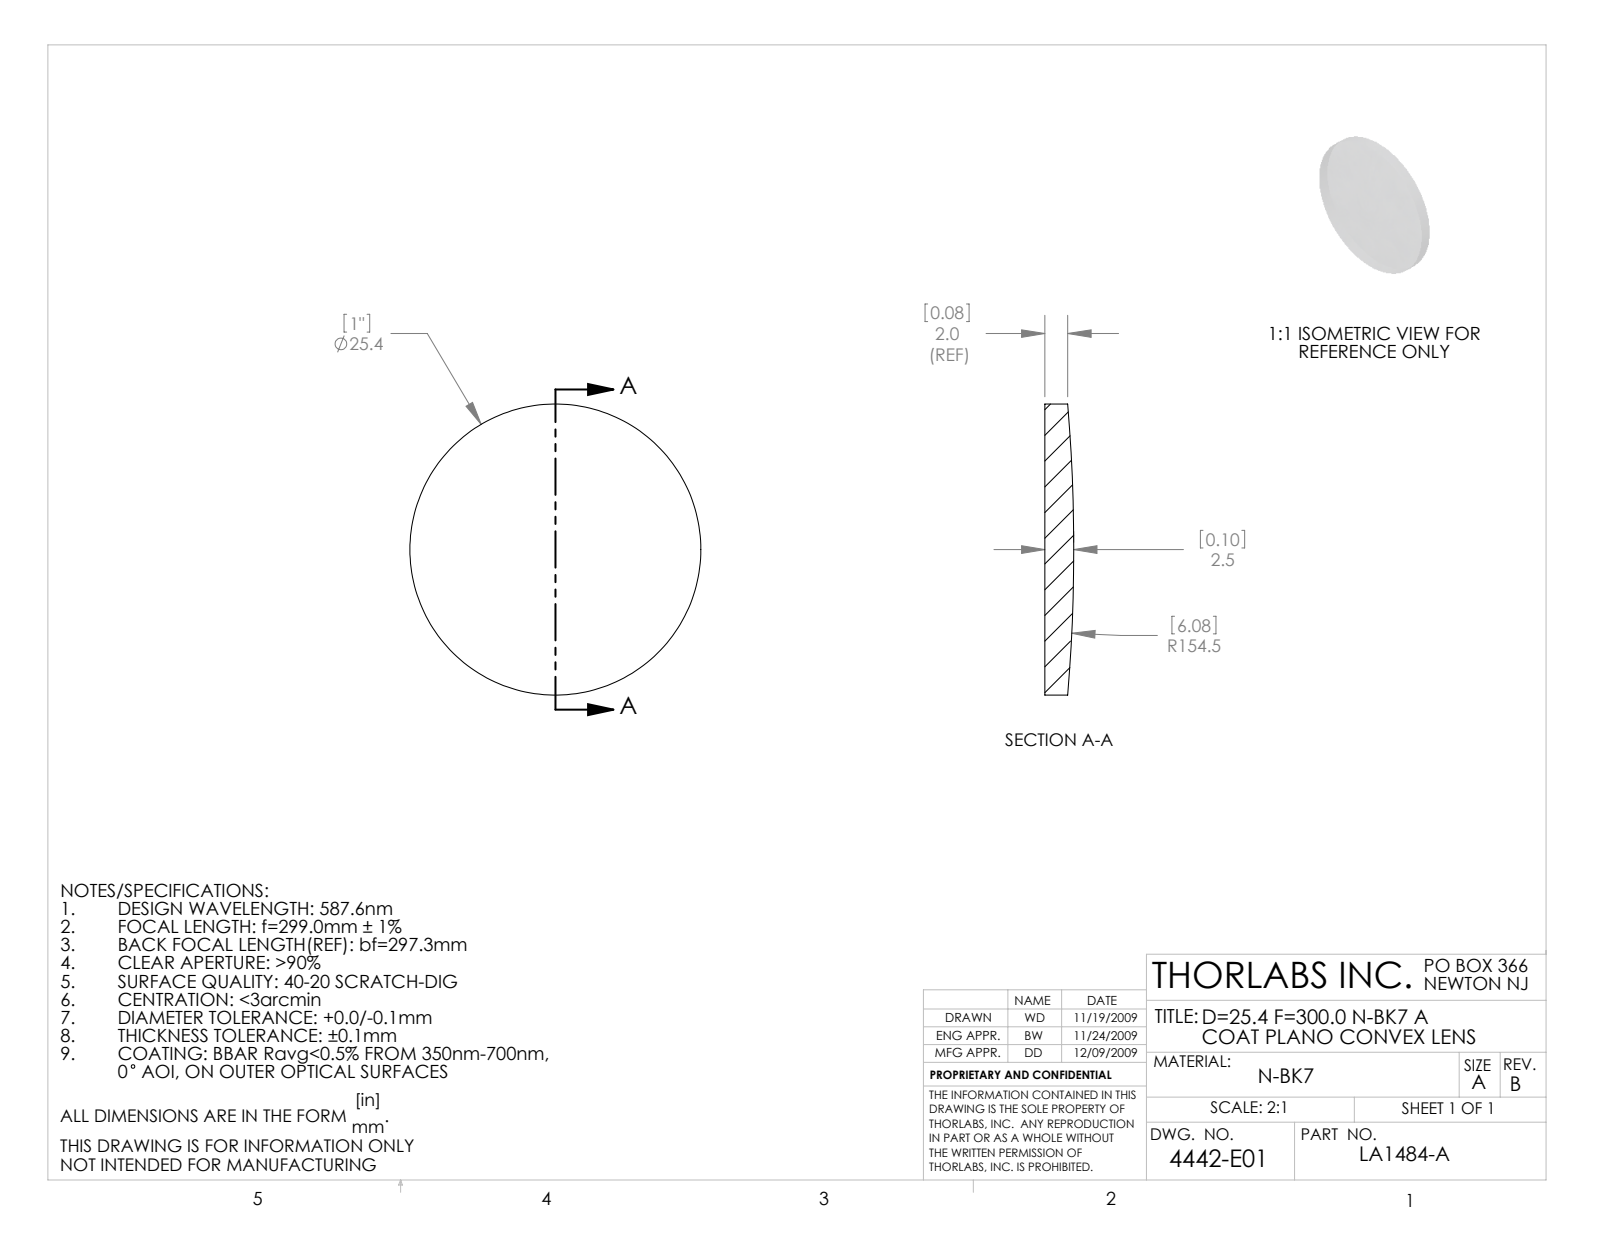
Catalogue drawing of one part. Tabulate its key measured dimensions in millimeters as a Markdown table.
| quantity | value |
| --- | --- |
| part name | 4442-E0W |
| STEP written by | SolidWorks 2009 (AUTOMOTIVE_DESIGN) |
| units | millimeters |
| bodies | 1 solid, 5 faces (1 planar, 2 cylindrical, 2 other) |
| overall size | 25.4 × 25.4 × 2.52 |
| volume | 1 145 mm³ |
| surface area | 1 174 mm² |
| round bosses / shafts (diameter × count) | 25.4 × 1 |
